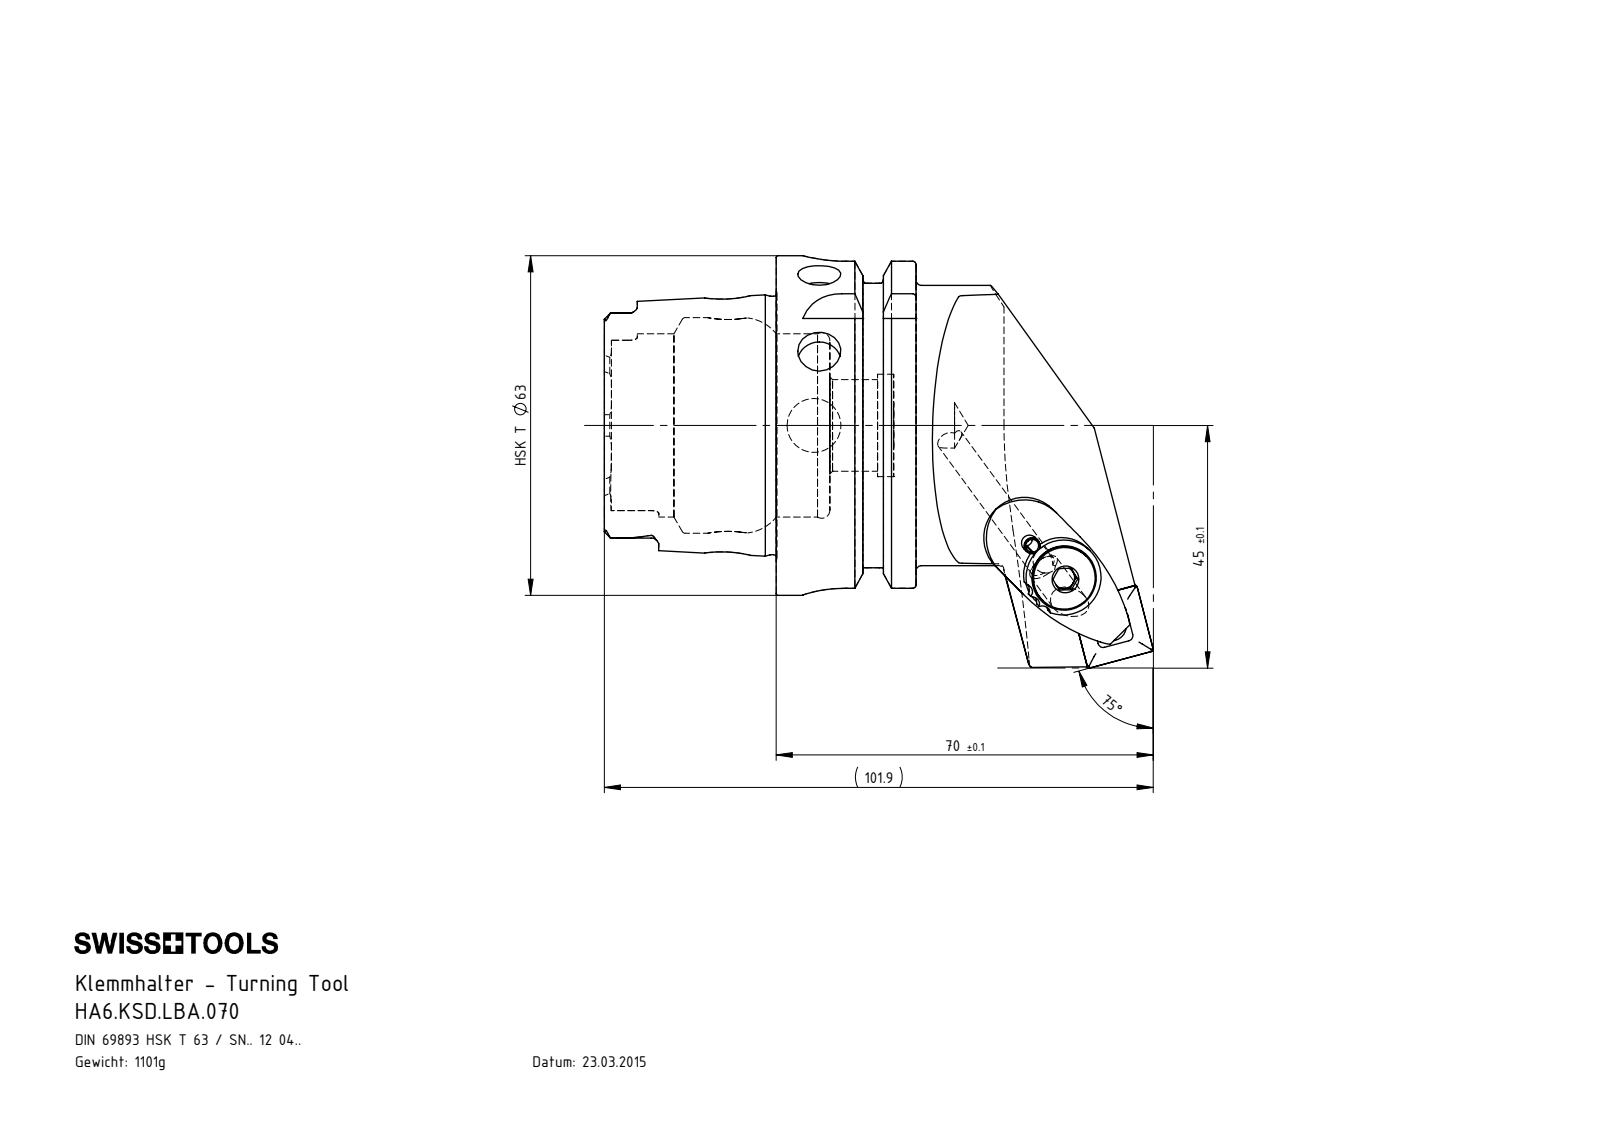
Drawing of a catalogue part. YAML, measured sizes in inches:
part_name: "ISO 13337 - 3 x 12_PreviewCfg; WCC-ER2.001.010_A; KVT_MB_600_060; HA6-KSD.LBA.070_A_Fertigbearbeitung (+6 more)"
step_written_by: "SolidWorks 2022 (CONFIG_CONTROL_DESIGN)"
units: inches
bodies: {solids: 10, faces: 481, planar: 126, cylindrical: 154, other: 201}
overall_size: [4.012, 3.012, 2.48]
volume: 8.523
surface_area: 54.25
round_holes:
  - {diameter: 0.079, count: 3}
  - {diameter: 0.197, count: 3}
  - {diameter: 0.165, count: 2}
  - {diameter: 0.244, count: 2}
  - {diameter: 0.315, count: 2}
  - {diameter: 0.094, count: 1}
  - {diameter: 0.118, count: 1}
  - {diameter: 0.203, count: 1}
  - {diameter: 0.236, count: 1}
  - {diameter: 0.256, count: 1}
  - {diameter: 0.276, count: 1}
  - {diameter: 0.295, count: 1}
round_bosses_or_shafts:
  - {diameter: 0.236, count: 2}
  - {diameter: 0.118, count: 2}
  - {diameter: 2.48, count: 1}
  - {diameter: 2.163, count: 1}
  - {diameter: 2.047, count: 1}
  - {diameter: 1.887, count: 1}
  - {diameter: 0.551, count: 1}
  - {diameter: 0.453, count: 1}
partial_cylinders:
  - {radius: 0.015, count: 6}
  - {radius: 0.027, count: 6}
  - {radius: 0.055, count: 6}
  - {radius: 0.016, count: 4}
  - {radius: 0.113, count: 4}
  - {radius: 0.315, count: 4}
  - {radius: 0.031, count: 3}
  - {radius: 0.059, count: 3}
face_to_face_distances: [1.022, 0.63, 0.392, 1.256, 1.648, 2.278, 2.079, 0.858, 0.467, 0.175]
hole_center_spacings: [0.591, 0.906, 0.298, 0.313, 0.315, 0.583, 0.305, 0.315]
